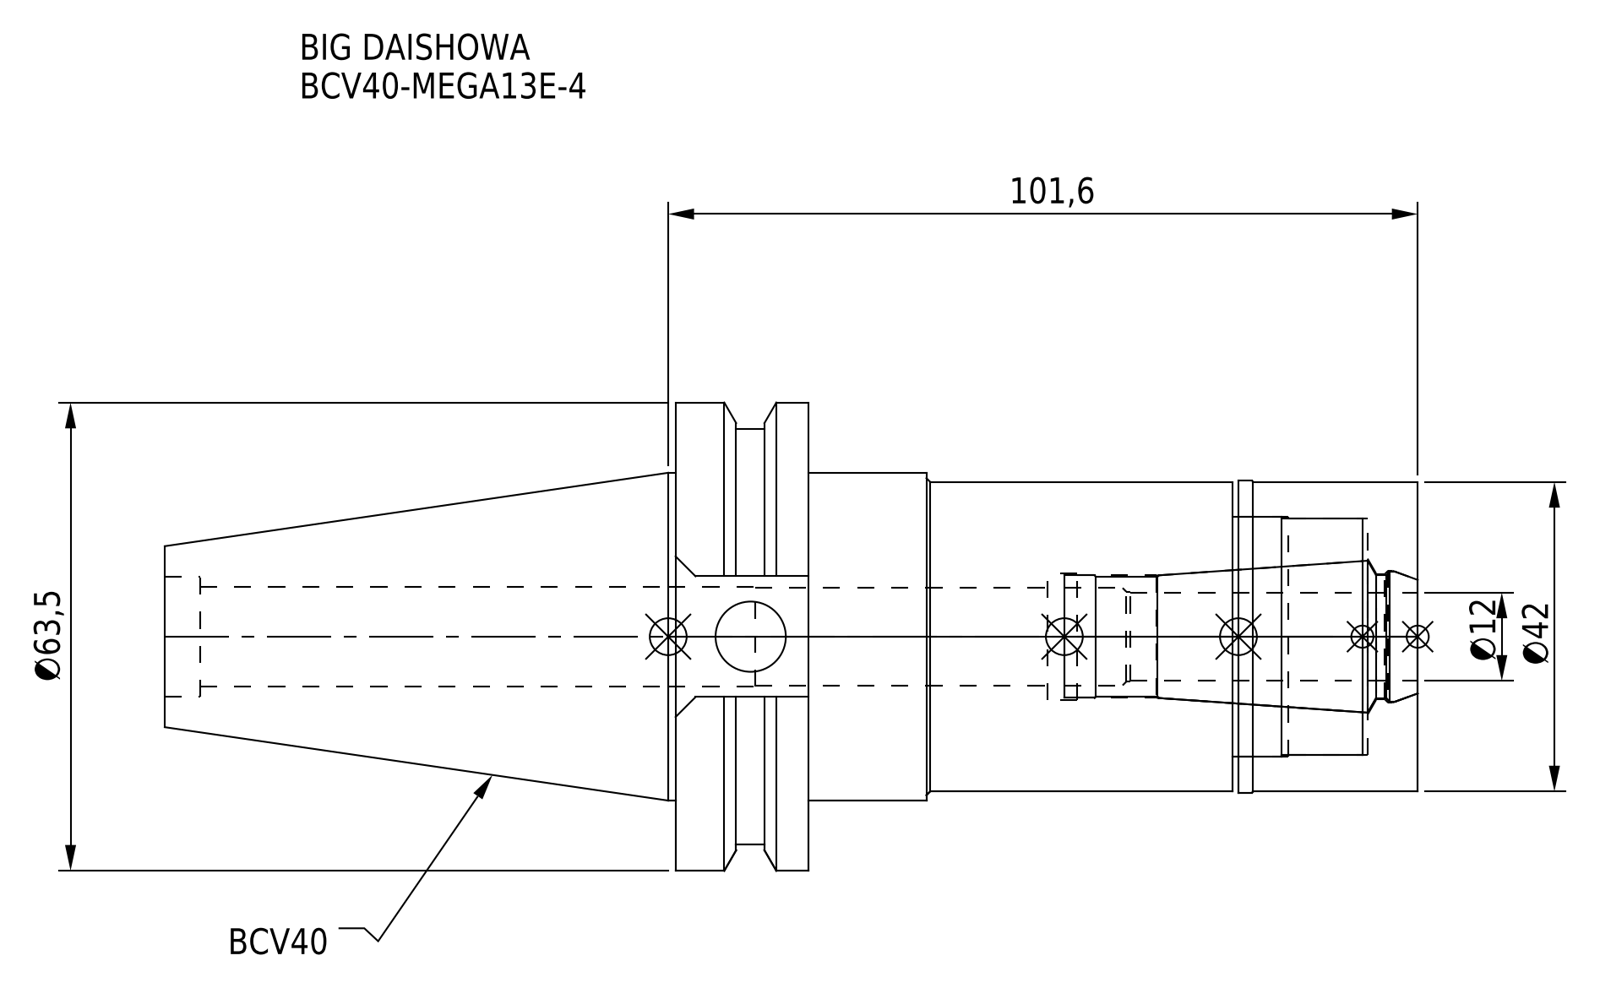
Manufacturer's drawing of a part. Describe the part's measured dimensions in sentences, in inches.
The part is named "BCV40-MEGA13E-4; BCV40ME13040-012_ASM.stp; DXF_TEMP_ASSY_ASM_4_ASM.stp; BCV40-MEGA13E-4_1.stp (+3 more)". Its 3-D file was written by "SolidWorks 2019 (CONFIG_CONTROL_DESIGN)". It is 2 solids with 90 faces: 30 planar, 42 cylindrical and 18 other. Overall it measures 6.687 by 2.5 by 2.415 inches. Its volume is 12.39 cubic inches and its surface area 63.99 square inches. Round holes: 1 of diameter 0.375, 1 of diameter 0.524, 1 of diameter 0.535, 1 of diameter 0.643, 1 of diameter 0.654, 1 of diameter 0.669, 1 of diameter 0.677, 1 of diameter 0.705, 1 of diameter 1.26, 1 of diameter 1.28. Round bosses or shafts: 1 of diameter 2.5, 1 of diameter 2.219, 1 of diameter 1.75, 1 of diameter 1.665, 1 of diameter 1.654. The main face-to-face distances are 0.711, 3.25, 3.961, 0.988, 0.957, 2.293, 3.004, 0.031, 2.262, 2.972.
